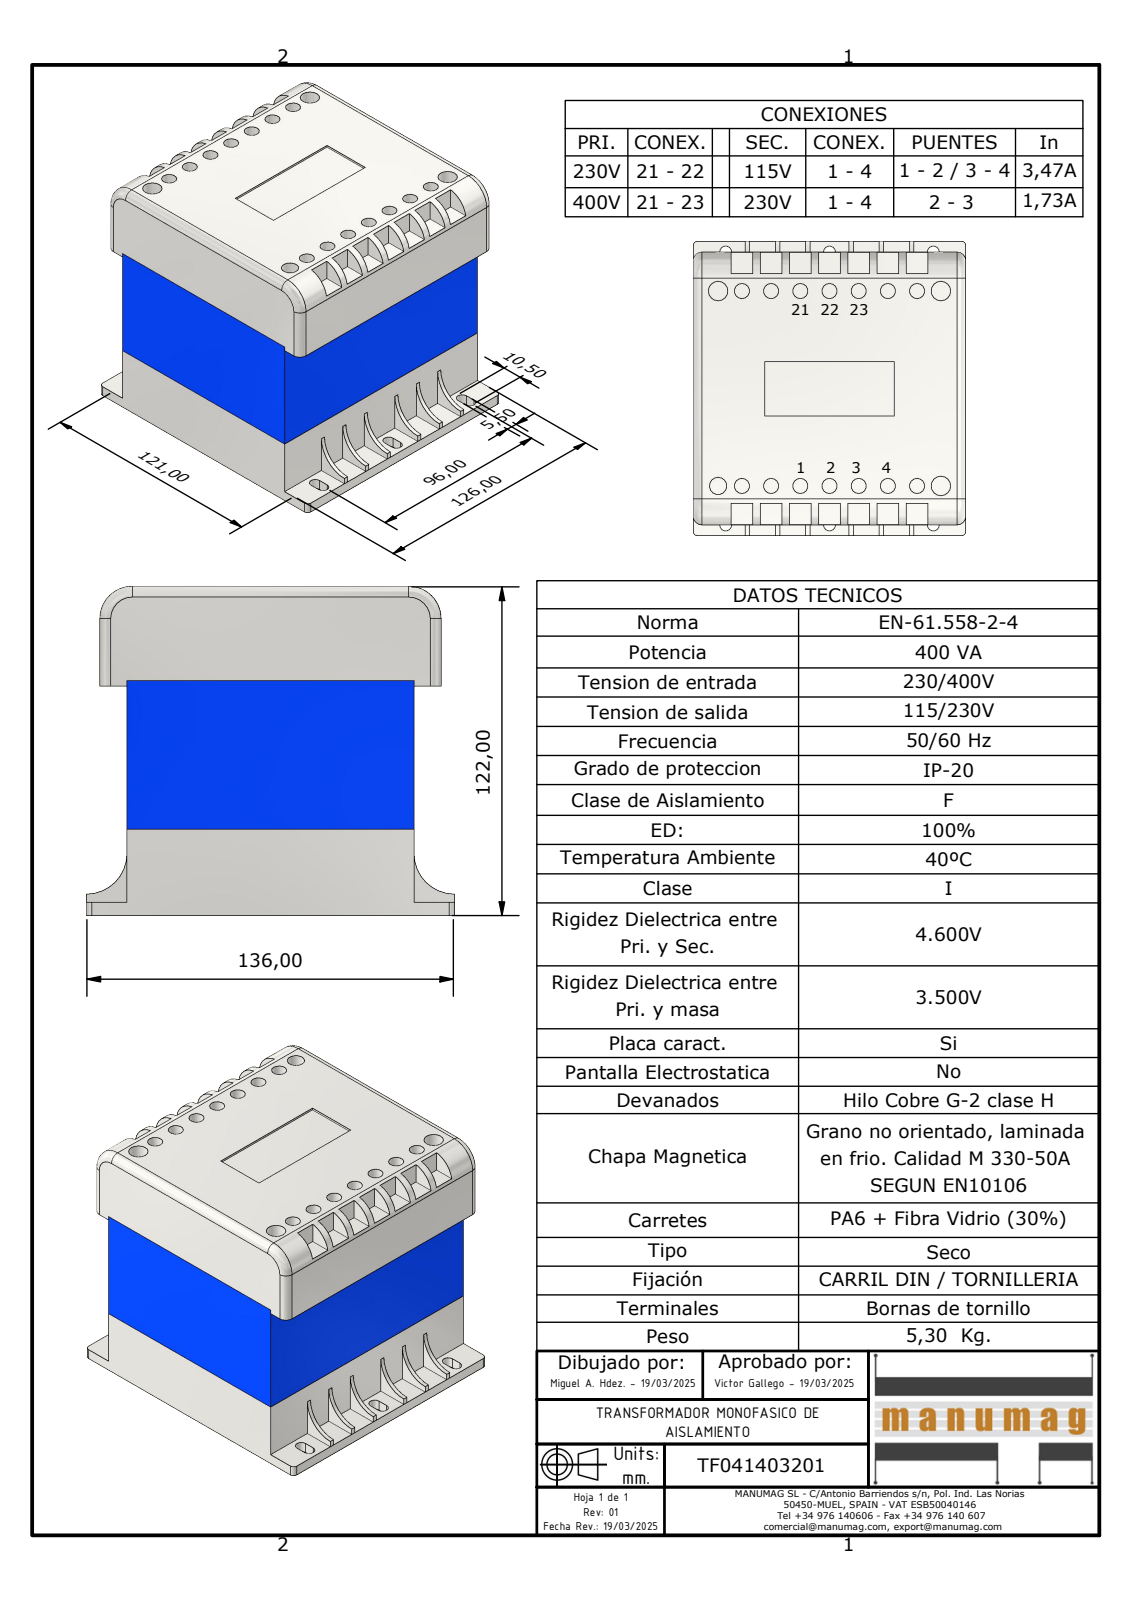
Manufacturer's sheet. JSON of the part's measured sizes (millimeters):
{"part_name": "TF041403201; INFERIOR EI120; CENTRAL EI120-50; SUPERIOR EI120", "step_written_by": "Autodesk Inventor 2023 (AUTOMOTIVE_DESIGN)", "units": "millimeters", "bodies": {"solids": 15, "faces": 244, "planar": 186, "cylindrical": 54, "other": 4}, "overall_size": [136, 126, 122], "volume_mm3": 656709, "surface_area_mm2": 172452, "round_holes": [[7, 14], [9, 3], [8, 1]], "partial_cylinders_radius": [[2.75, 12], [4, 6], [2, 4], [12, 2], [15, 2]], "face_to_face_distances": [1, 105, 5, 125, 126, 87, 82, 106, 104, 122], "hole_center_spacings": [13.5, 91.01, 27, 93.96, 90, 40.5, 98.69, 54]}
